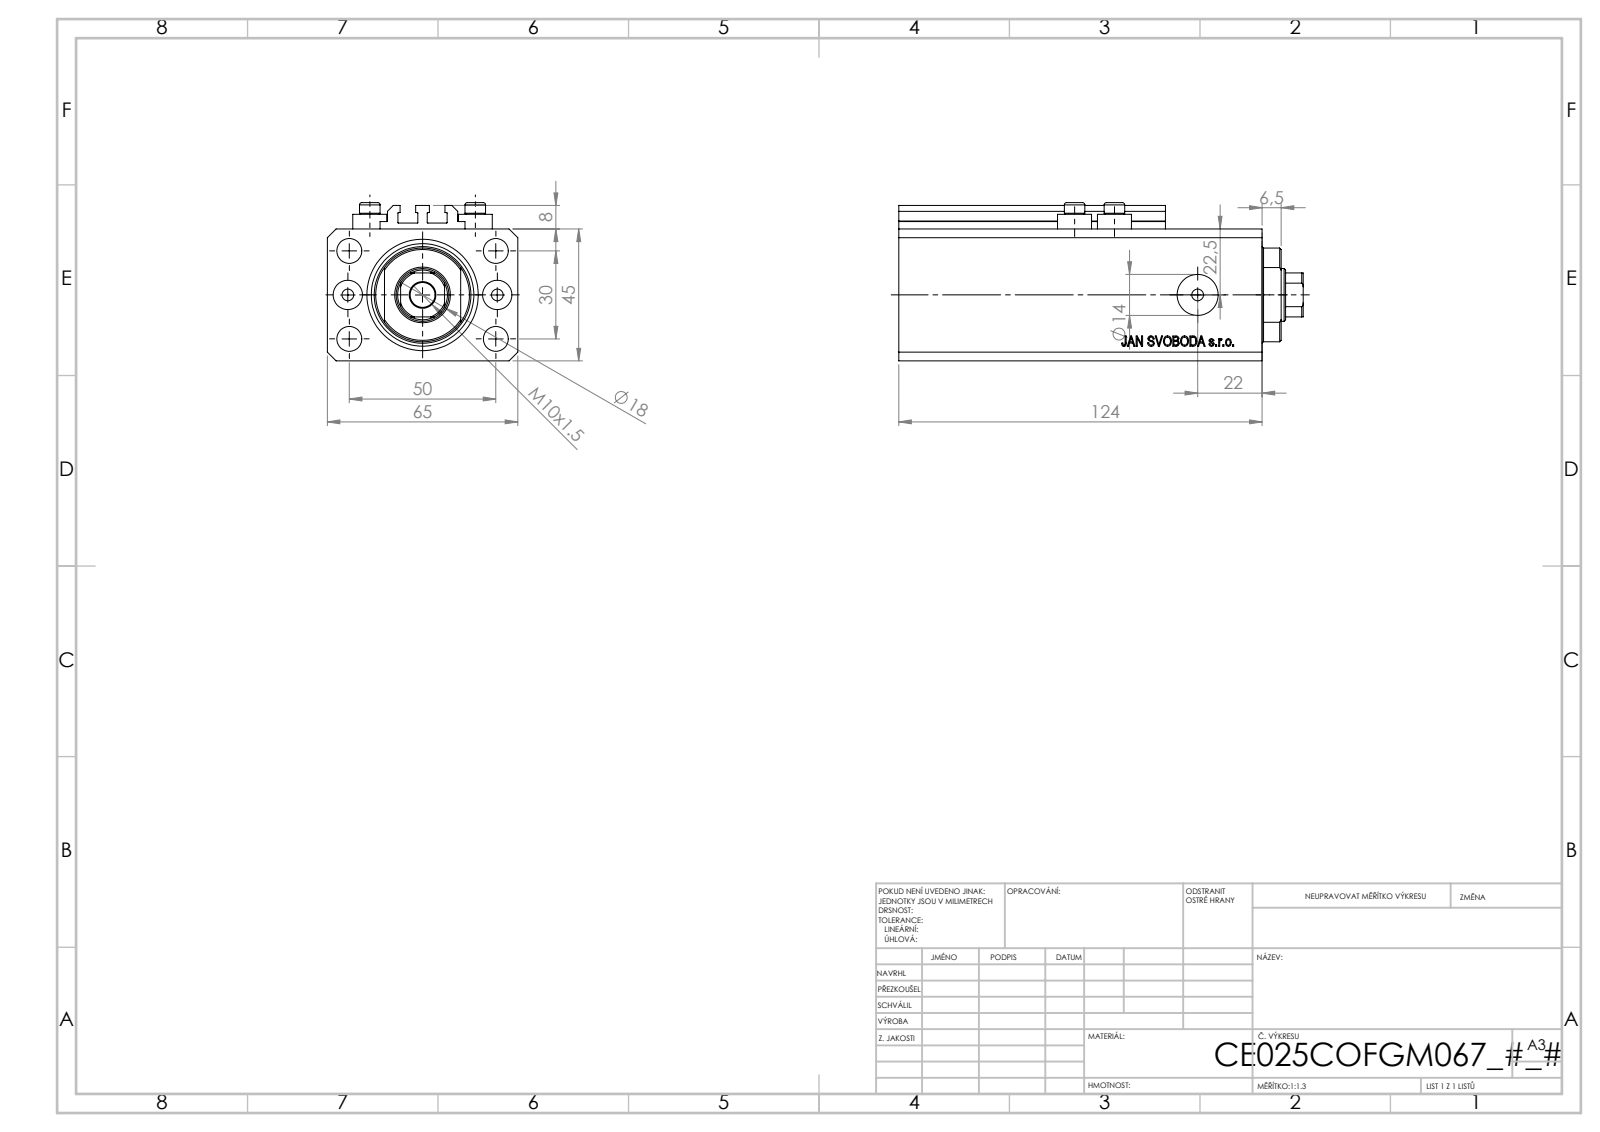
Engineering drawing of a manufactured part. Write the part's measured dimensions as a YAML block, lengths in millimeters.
part_name: "V250CE_C_VCP; ALLEN BOLT V250CE; V250CE_C_Body; V250CE_VC_C"
step_written_by: "SolidWorks 2019 (CONFIG_CONTROL_DESIGN)"
units: millimeters
bodies: {solids: 8, faces: 1034, planar: 504, cylindrical: 86, other: 444}
overall_size: [138, 65, 54]
volume: 332719
surface_area: 83382
round_holes:
  - {diameter: 4, count: 8}
  - {diameter: 8.5, count: 5}
  - {diameter: 10, count: 2}
  - {diameter: 14, count: 2}
  - {diameter: 18, count: 1}
  - {diameter: 25, count: 1}
  - {diameter: 38, count: 1}
round_bosses_or_shafts:
  - {diameter: 11.6, count: 4}
  - {diameter: 7, count: 4}
partial_cylinders:
  - {radius: 0.2, count: 10}
  - {radius: 8.5, count: 1}
  - {radius: 16, count: 1}
face_to_face_distances: [45, 65, 14, 47, 110, 124, 2.5, 2, 10, 20.5]
hole_center_spacings: [15.01, 29.15, 52.68, 13.6, 25.5, 30, 36, 38.48]
